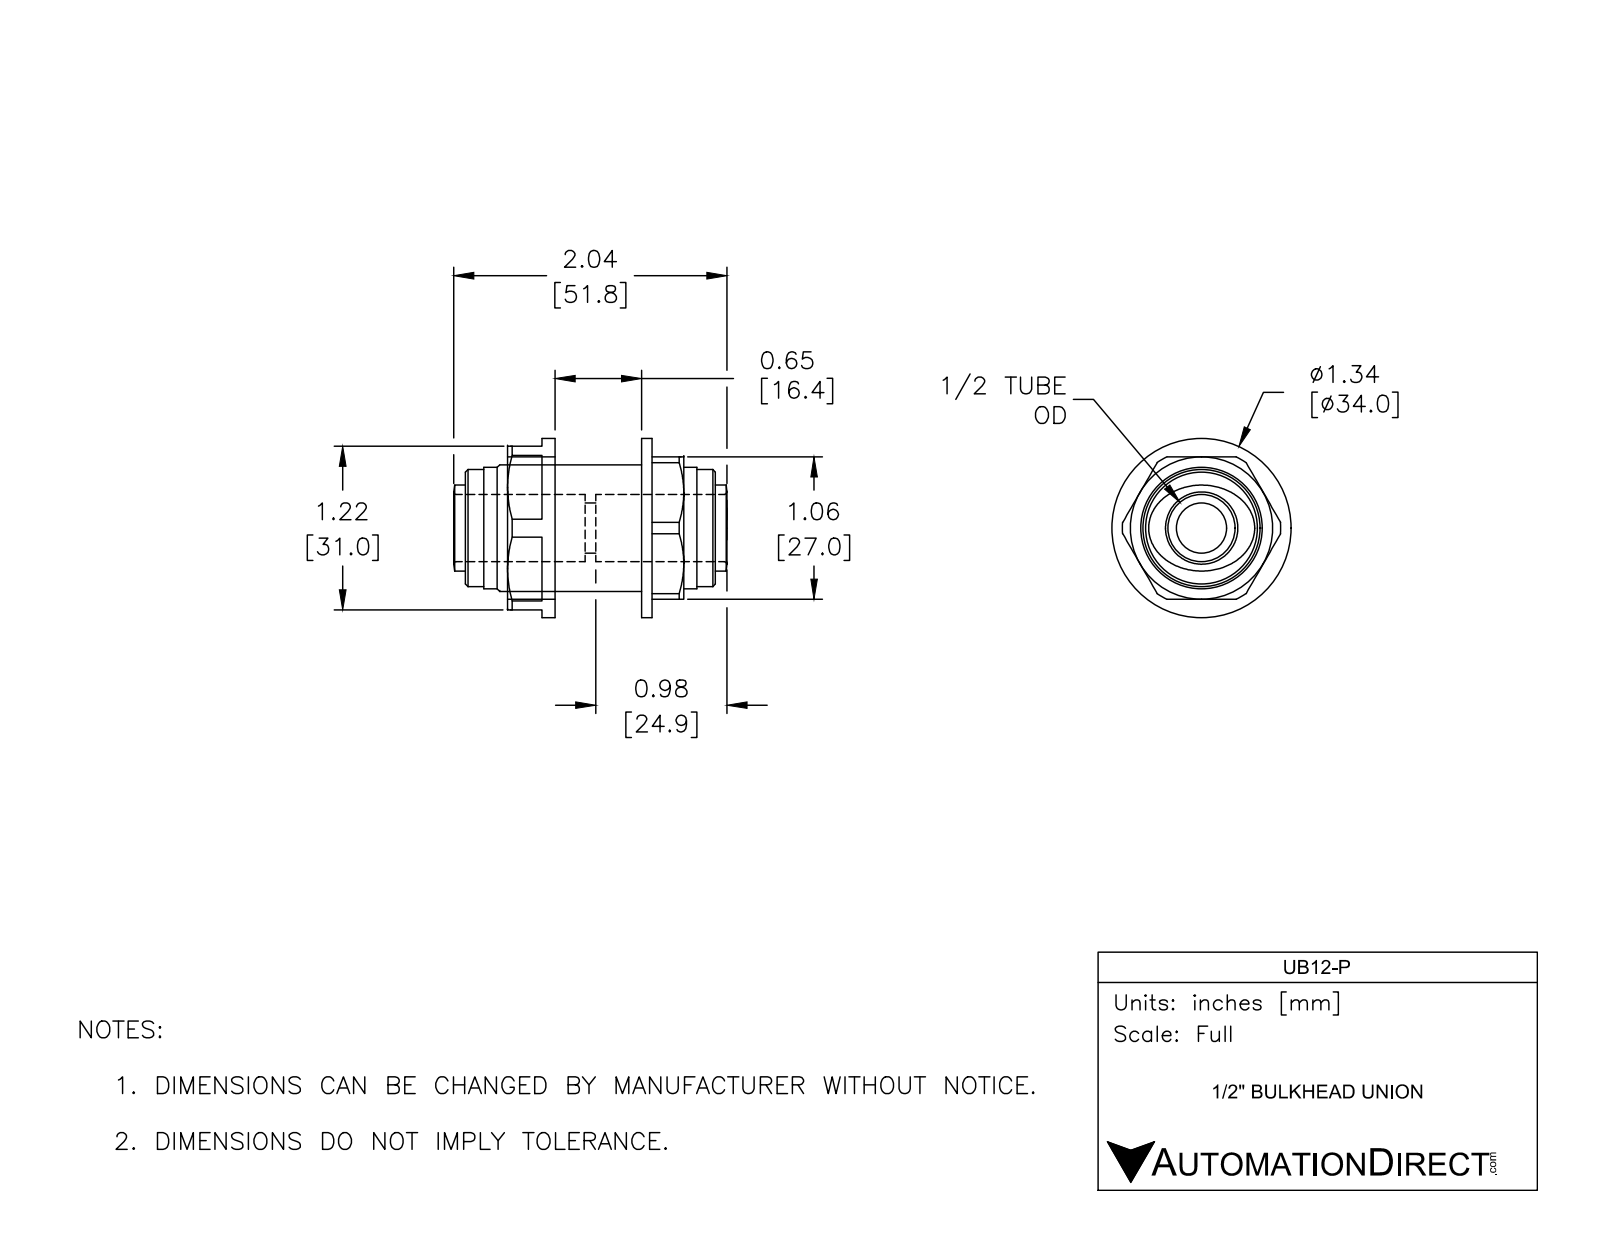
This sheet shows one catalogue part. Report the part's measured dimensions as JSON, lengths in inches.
{"part_name": "UB12-P", "step_written_by": "SolidWorks 2017 (AUTOMOTIVE_DESIGN)", "units": "inches", "bodies": {"solids": 1, "faces": 90, "planar": 31, "cylindrical": 29, "other": 30}, "overall_size": [2.039, 1.339, 1.339], "volume_in3": 1.361, "surface_area_in2": 13.91, "round_holes": [[0.374, 1], [0.5, 1], [1.063, 1]], "round_bosses_or_shafts": [[1.339, 1], [0.906, 1], [0.874, 1]], "partial_cylinders_radius": [[0.591, 1]], "face_to_face_distances": [0.079, 1.142, 0.646, 0.945, 0.724, 1.22, 0.236, 0.315, 1.315, 0.138]}
